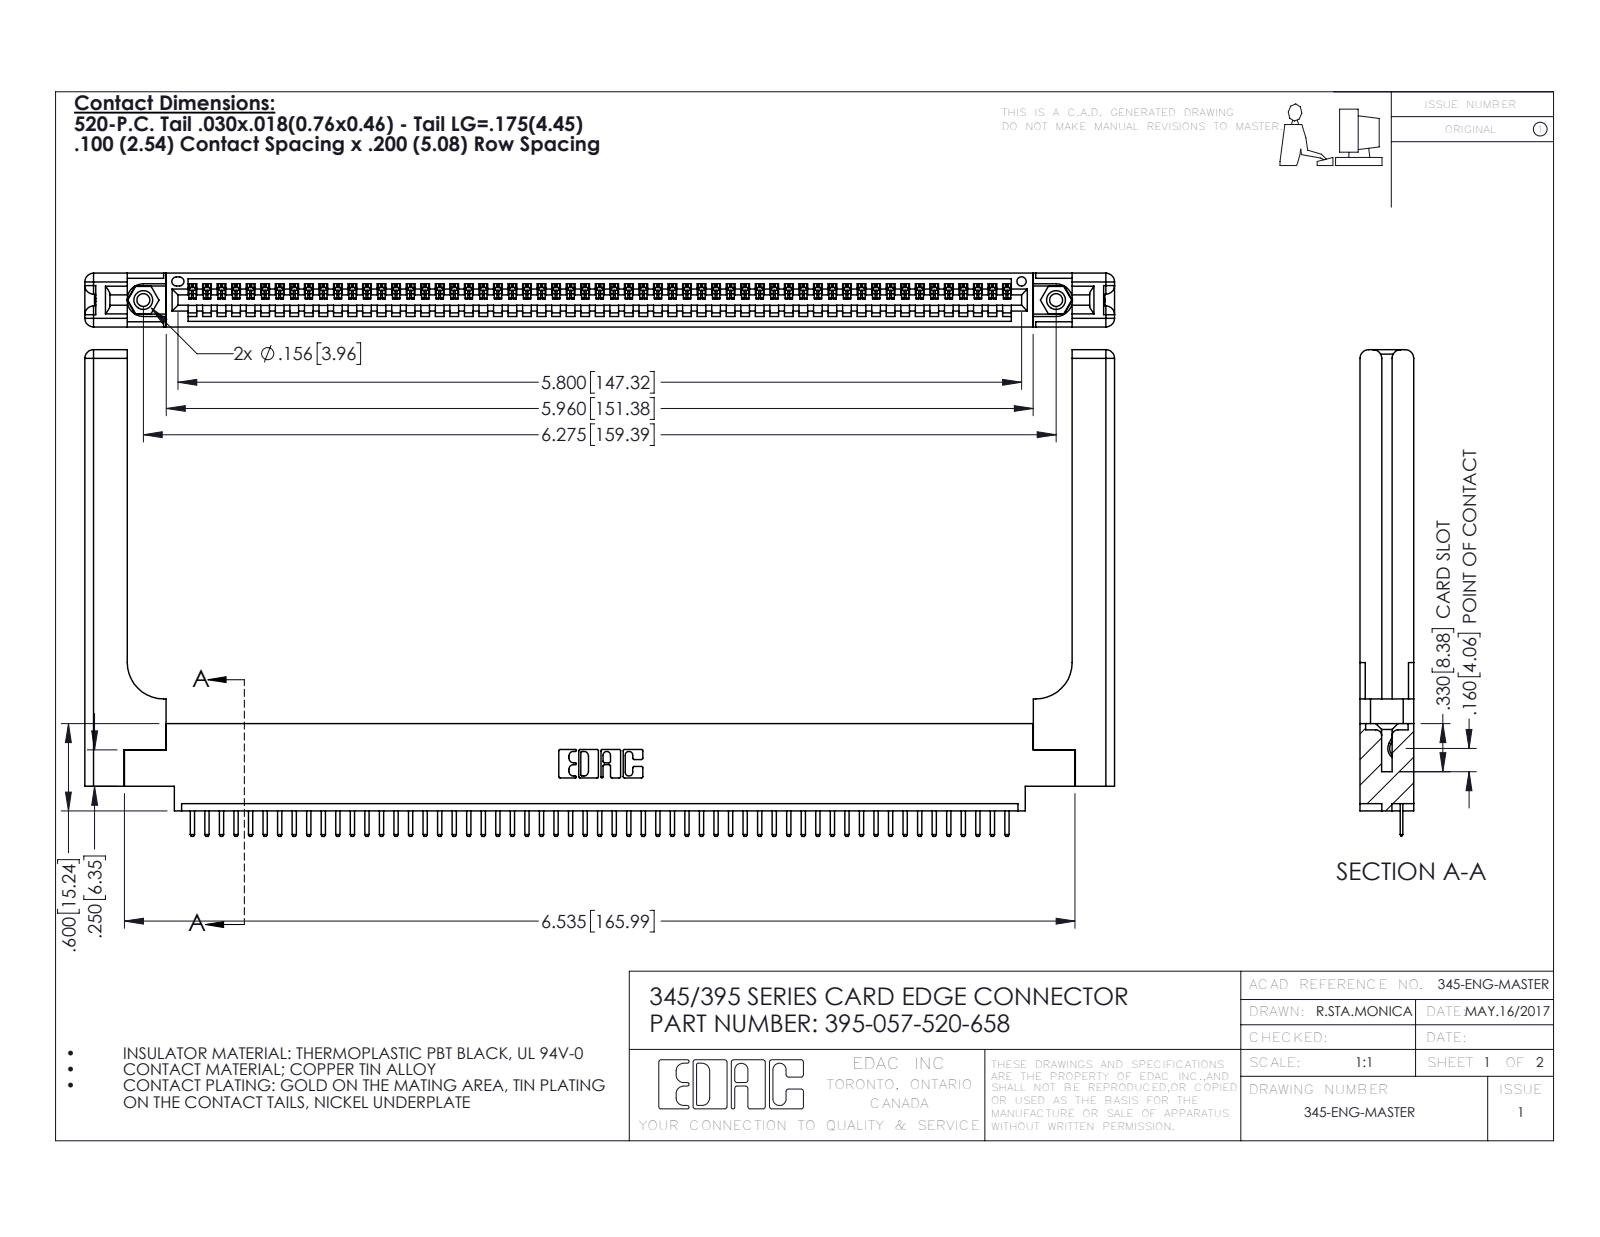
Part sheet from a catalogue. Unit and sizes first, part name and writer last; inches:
Units: inches
Overall size (bounding box): 7.079 × 3.345 × 0.37
Round holes (diameter × count): ⌀0.089 ×2, ⌀0.125 ×2, ⌀0.156 ×2, ⌀0.064 ×1
Round bosses / shafts (diameter × count): ⌀0.155 ×2
Partial cylindrical surfaces — rounded edges, fillets, slot ends (radius × count): R0.01 ×116, R0.006 ×114, R0.01 ×22, R0.06 ×16, R0.007 ×6, R0.031 ×6, R0.026 ×3, R0.03 ×2
Main face-to-face distances: 0.37, 0.072, 0.298, 0.098, 0.272, 0.025, 0.2, 0.225, 0.148, 0.15
Hole centre spacings: 0.27, 6.039, 6.275
Volume: 1.552 in³ · Surface area: 42.76 in²
Bodies: 62 solids, 3920 faces (2626 planar, 1234 cylindrical, 60 other)
Part name (STEP PRODUCT): 345-220-058_345-220-058; 395-057-520-658; 345 Part_0.170 Offset - 0.156 Dia-TH; 345-292-001_345-293-120 (+1 more)
STEP written by: SolidWorks 2016 (CONFIG_CONTROL_DESIGN)
